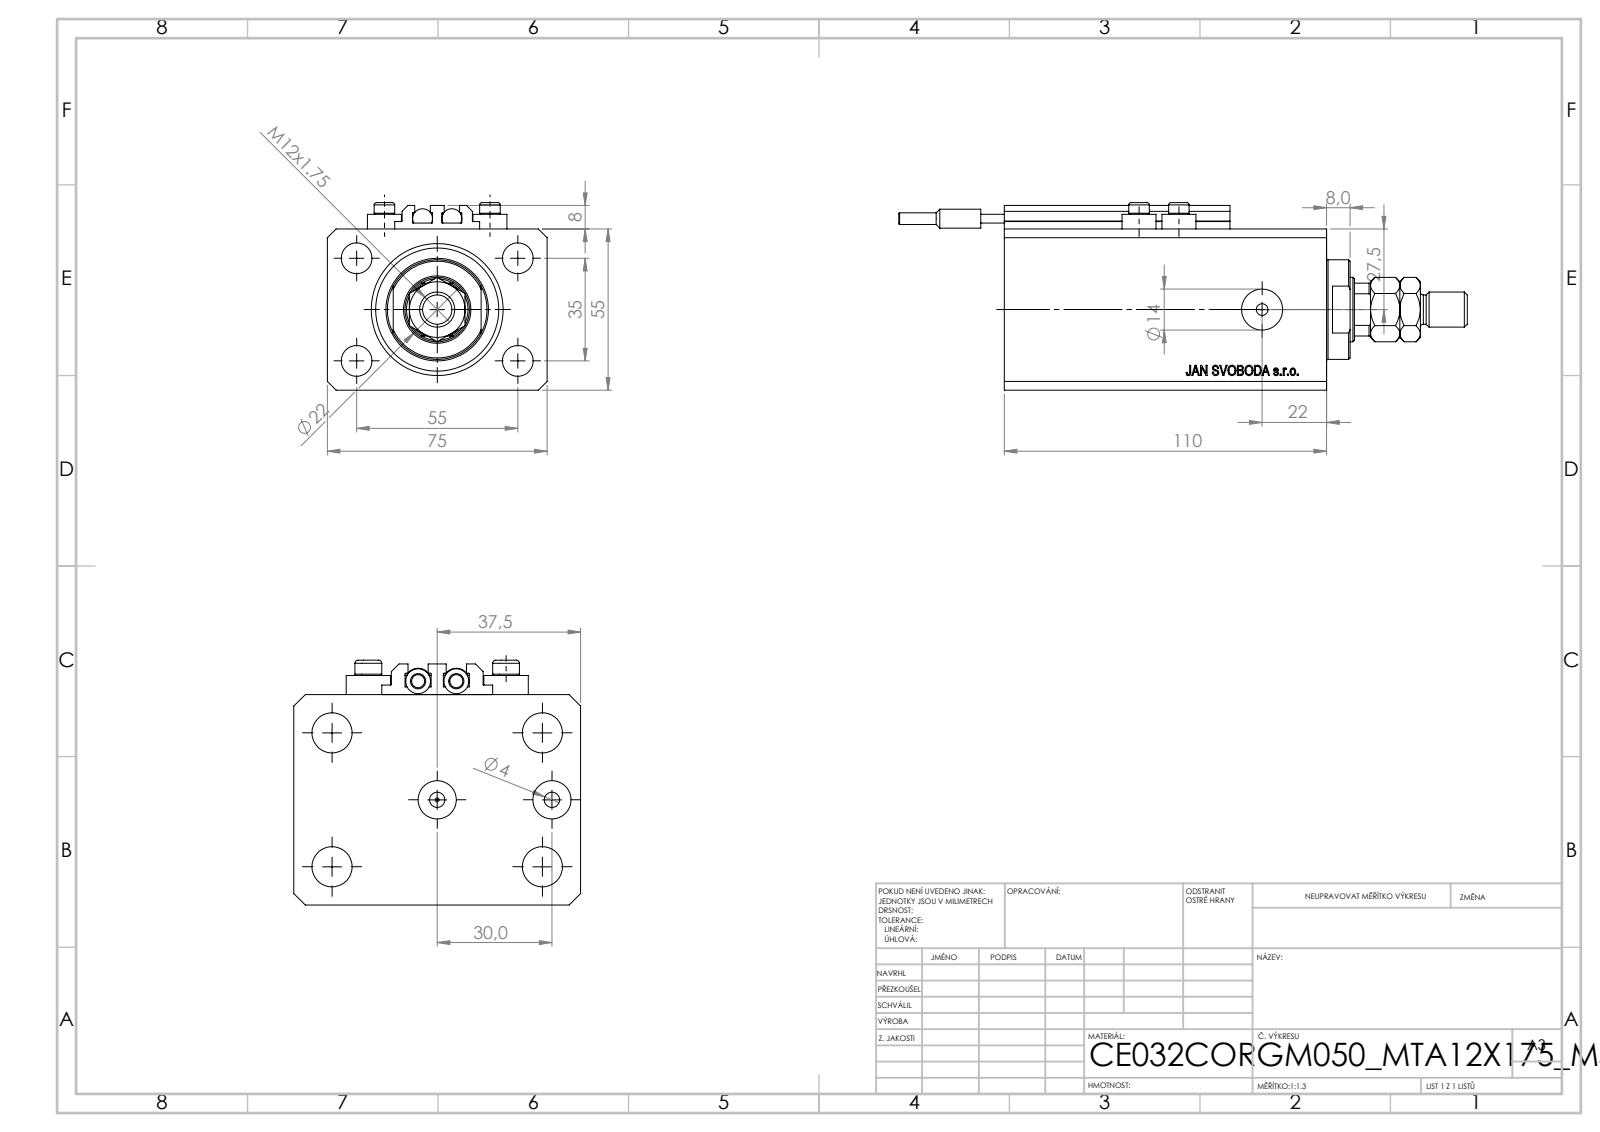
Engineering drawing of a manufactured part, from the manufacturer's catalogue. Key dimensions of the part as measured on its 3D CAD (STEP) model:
Part name (STEP PRODUCT): SWITCH_V250CE; V250CE_C_Body; MTA; V250CE_C_VCP (+2 more)
STEP written by: SolidWorks 2019 (CONFIG_CONTROL_DESIGN)
Units: millimetres
Bodies: 11 solids, 1139 faces (551 planar, 104 cylindrical, 484 other)
Overall size (bounding box): 194 × 75 × 64
Volume: 418 995 mm³ · Surface area: 96 675 mm²
Round holes (diameter × count): ⌀4 ×8, ⌀10.5 ×5, ⌀10 ×2, ⌀14 ×2, ⌀1.25 ×1, ⌀22 ×1, ⌀32 ×1, ⌀45 ×1
Round bosses / shafts (diameter × count): ⌀11.6 ×4, ⌀7 ×4, ⌀6.8 ×2, ⌀6.5 ×2, ⌀4 ×2, ⌀34 ×1, ⌀12 ×1
Partial cylindrical surfaces — rounded edges, fillets, slot ends (radius × count): R0.2 ×10, R10.5 ×1
Main face-to-face distances: 55, 75, 110, 15, 95, 3, 9.9, 85.1, 100.1, 2.5
Hole centre spacings: 32.6, 13.6, 17.68, 35, 36, 38.48, 55, 60.1
